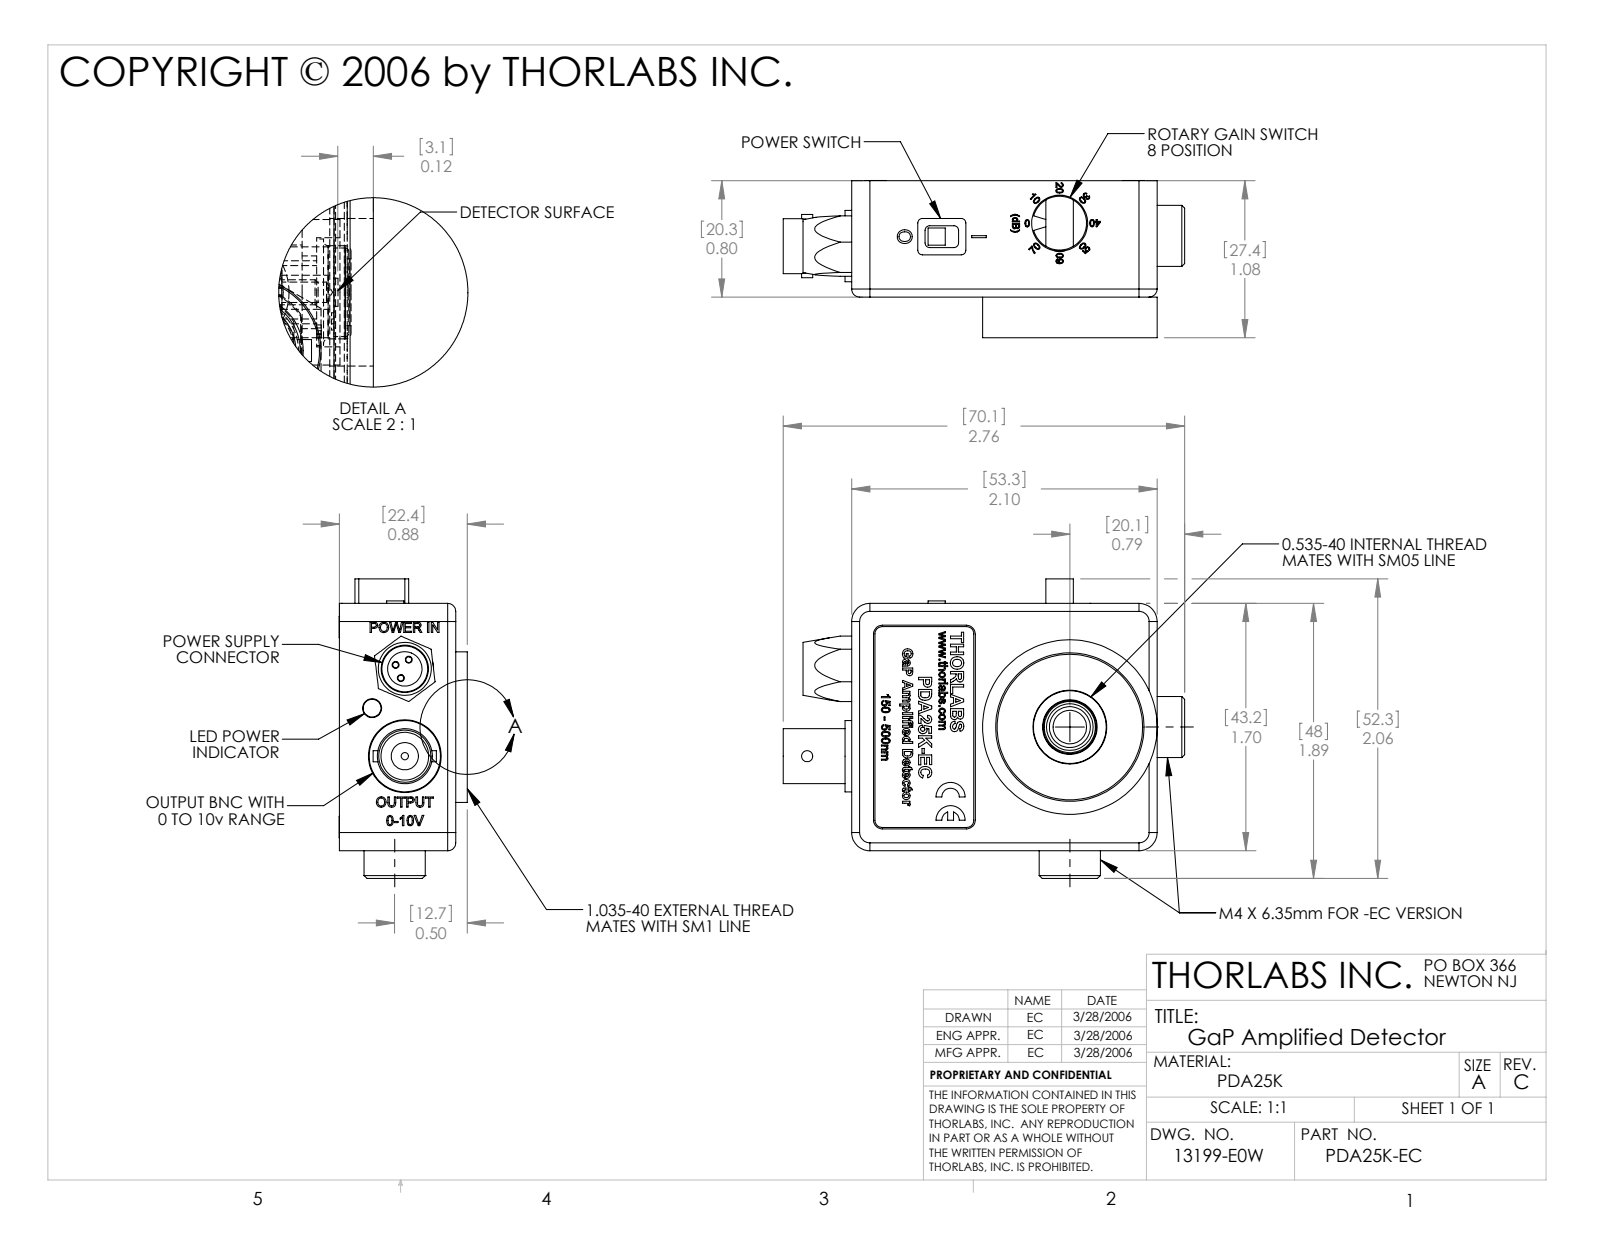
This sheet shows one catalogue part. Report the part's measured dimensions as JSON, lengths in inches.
{"part_name": "13199-E0W", "step_written_by": "SolidWorks 2011 (CONFIG_CONTROL_DESIGN)", "units": "inches", "bodies": {"solids": 0, "faces": 547, "planar": 348, "cylindrical": 94, "other": 105}, "overall_size": [2.761, 2.058, 1.082], "round_holes": [[0.039, 3], [0.13, 2], [0.05, 1], [0.13, 1], [0.23, 1], [0.315, 1], [0.325, 1], [0.328, 1], [0.375, 1], [0.385, 1], [0.5, 1], [0.507, 1]], "round_bosses_or_shafts": [[0.147, 4], [0.42, 2], [1.2, 1], [0.49, 1], [0.378, 1], [0.37, 1], [0.32, 1], [0.236, 1]], "partial_cylinders_radius": [[0.031, 8], [0.095, 8], [0.125, 6], [0.055, 4], [0.062, 3], [0.05, 2], [0.06, 1], [0.063, 1]], "face_to_face_distances": [0.565, 0.063, 0.502, 0.502, 0.439, 0.063, 0.298, 0.8, 0.737, 0.235], "hole_center_spacings": [0.069, 0.098, 0.112, 0.138, 0.202, 0.212, 0.286, 0.339]}
